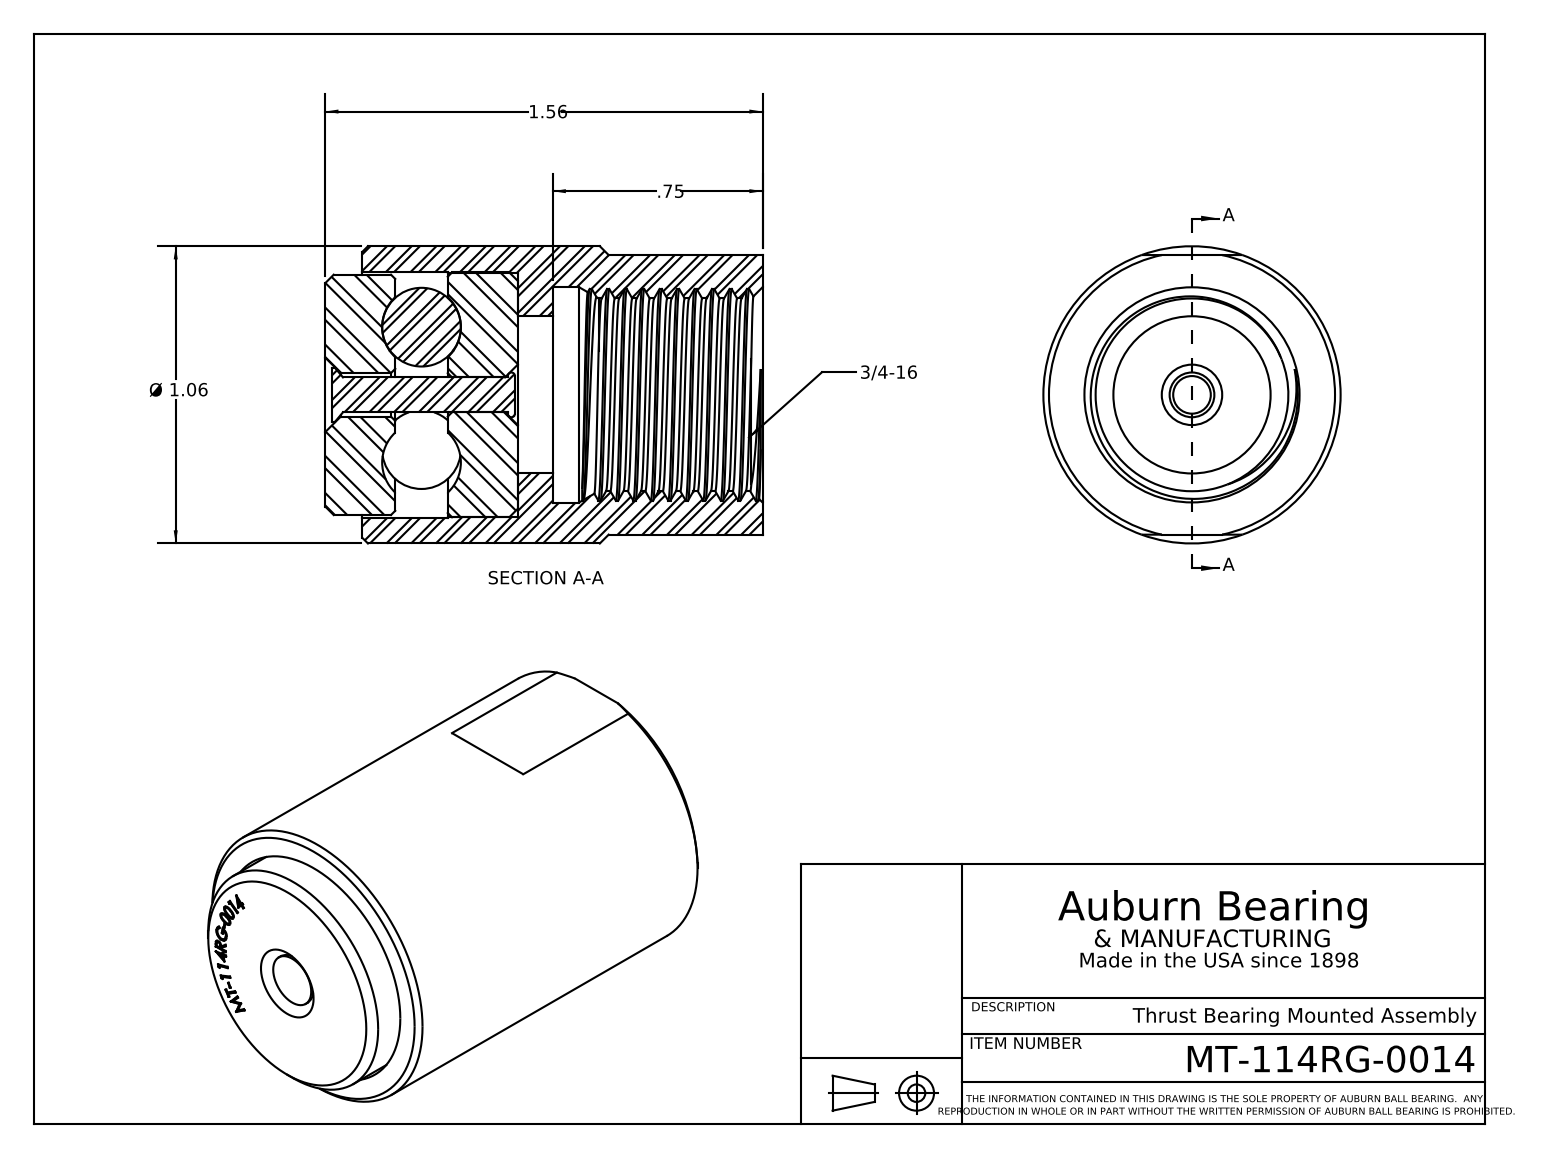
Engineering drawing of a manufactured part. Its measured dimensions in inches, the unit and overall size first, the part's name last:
Units: inches
Overall size (bounding box): 1.563 × 1.063 × 1.063
Round holes (diameter × count): ⌀0.125 ×1, ⌀0.156 ×1, ⌀0.562 ×1, ⌀0.689 ×1, ⌀0.77 ×1, ⌀0.874 ×1, ⌀0.878 ×1
Round bosses / shafts (diameter × count): ⌀1.063 ×1, ⌀0.875 ×1, ⌀0.859 ×1, ⌀0.192 ×1
Main face-to-face distances: 0.688, 0.25, 0.438, 1.563, 0.875, 1.125, 0.813, 0.375, 0.125, 0.75
Volume: 0.909 in³ · Surface area: 15.67 in²
Bodies: 9 solids, 245 faces (124 planar, 41 cylindrical, 80 other)
Part name (STEP PRODUCT): MT-114RG-0014
STEP written by: SolidWorks 2020 (CONFIG_CONTROL_DESIGN)
